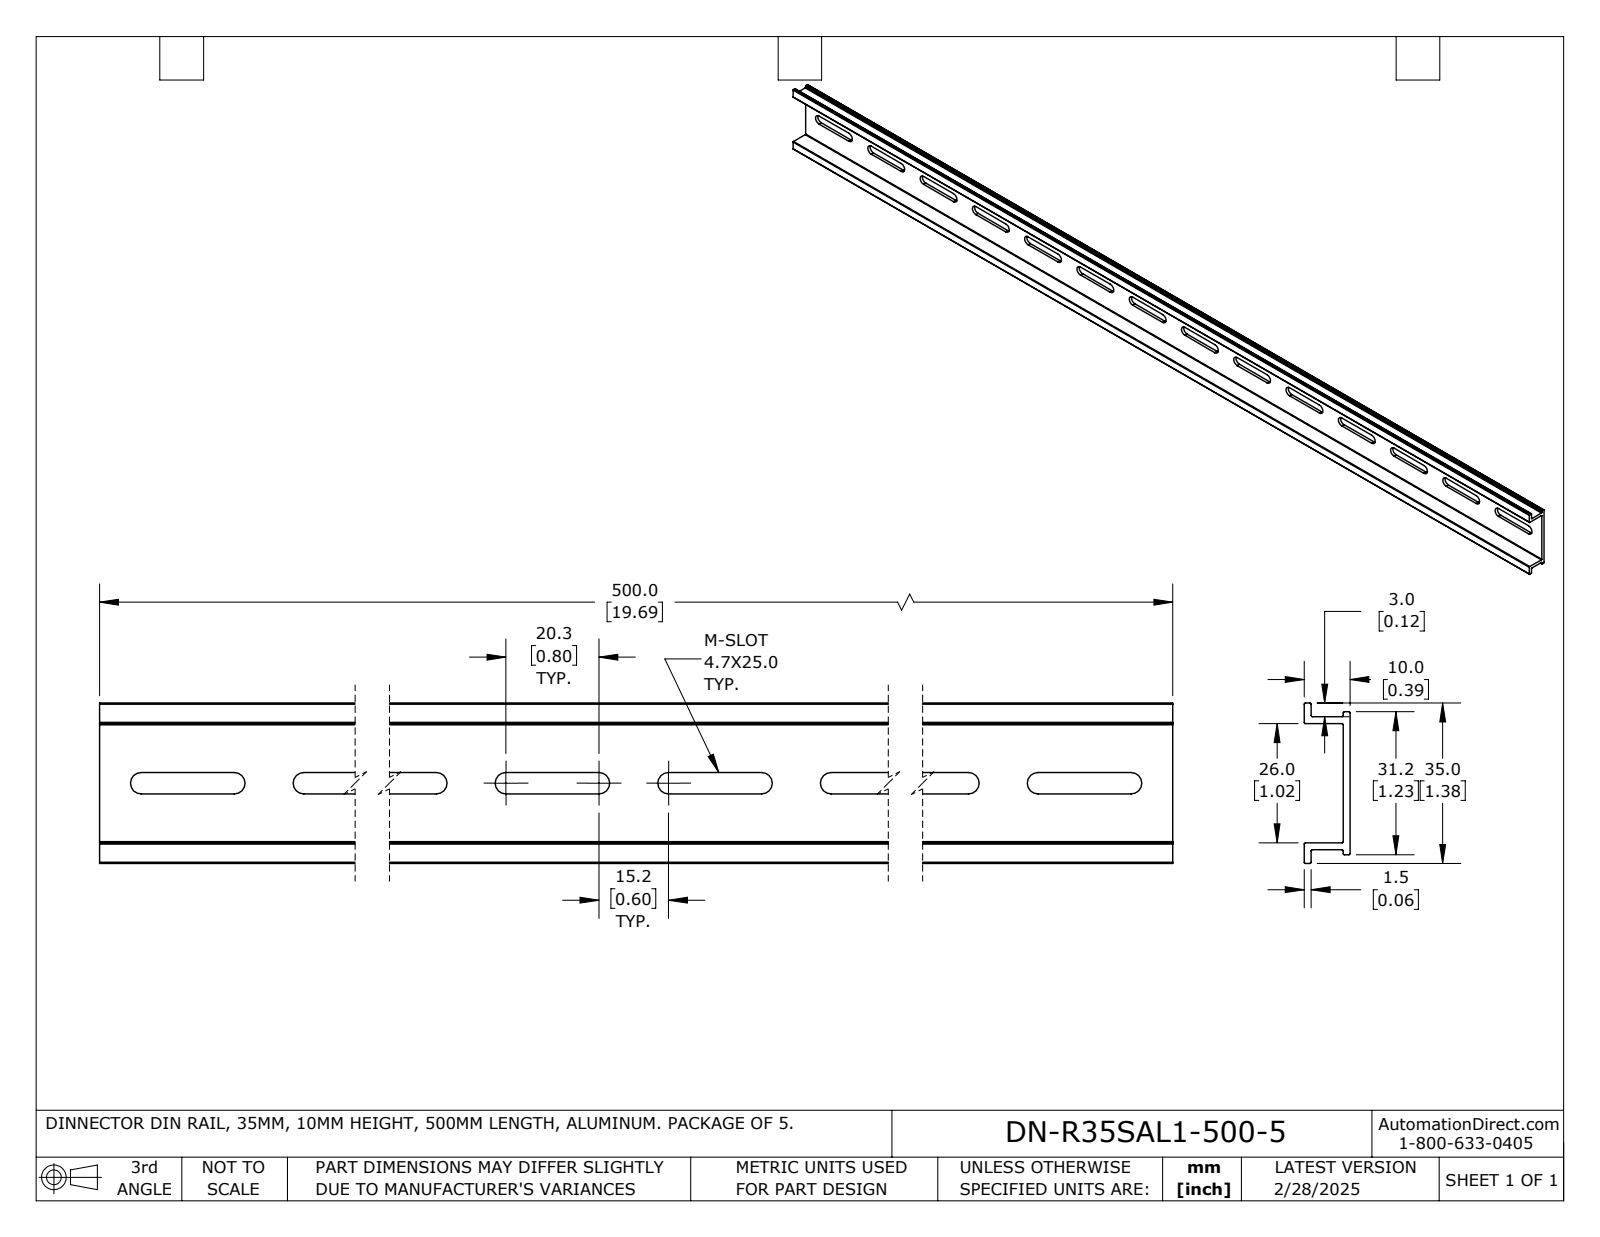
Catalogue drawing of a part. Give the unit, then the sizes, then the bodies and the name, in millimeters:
Units: millimetres
Overall size (bounding box): 500 × 35 × 10
Partial cylindrical surfaces — rounded edges, fillets, slot ends (radius × count): R2.35 ×28, R0.27 ×16
Main face-to-face distances: 1.5, 27.5, 8.5, 26, 10, 29, 7, 1.1, 2.6, 28.6
Volume: 38 251 mm³ · Surface area: 52 948 mm²
Bodies: 1 solid, 90 faces (46 planar, 44 cylindrical, 0 other)
Part name (STEP PRODUCT): DN-R35SAL1-500-5_Default
STEP written by: SolidWorks 2024 (CONFIG_CONTROL_DESIGN)
